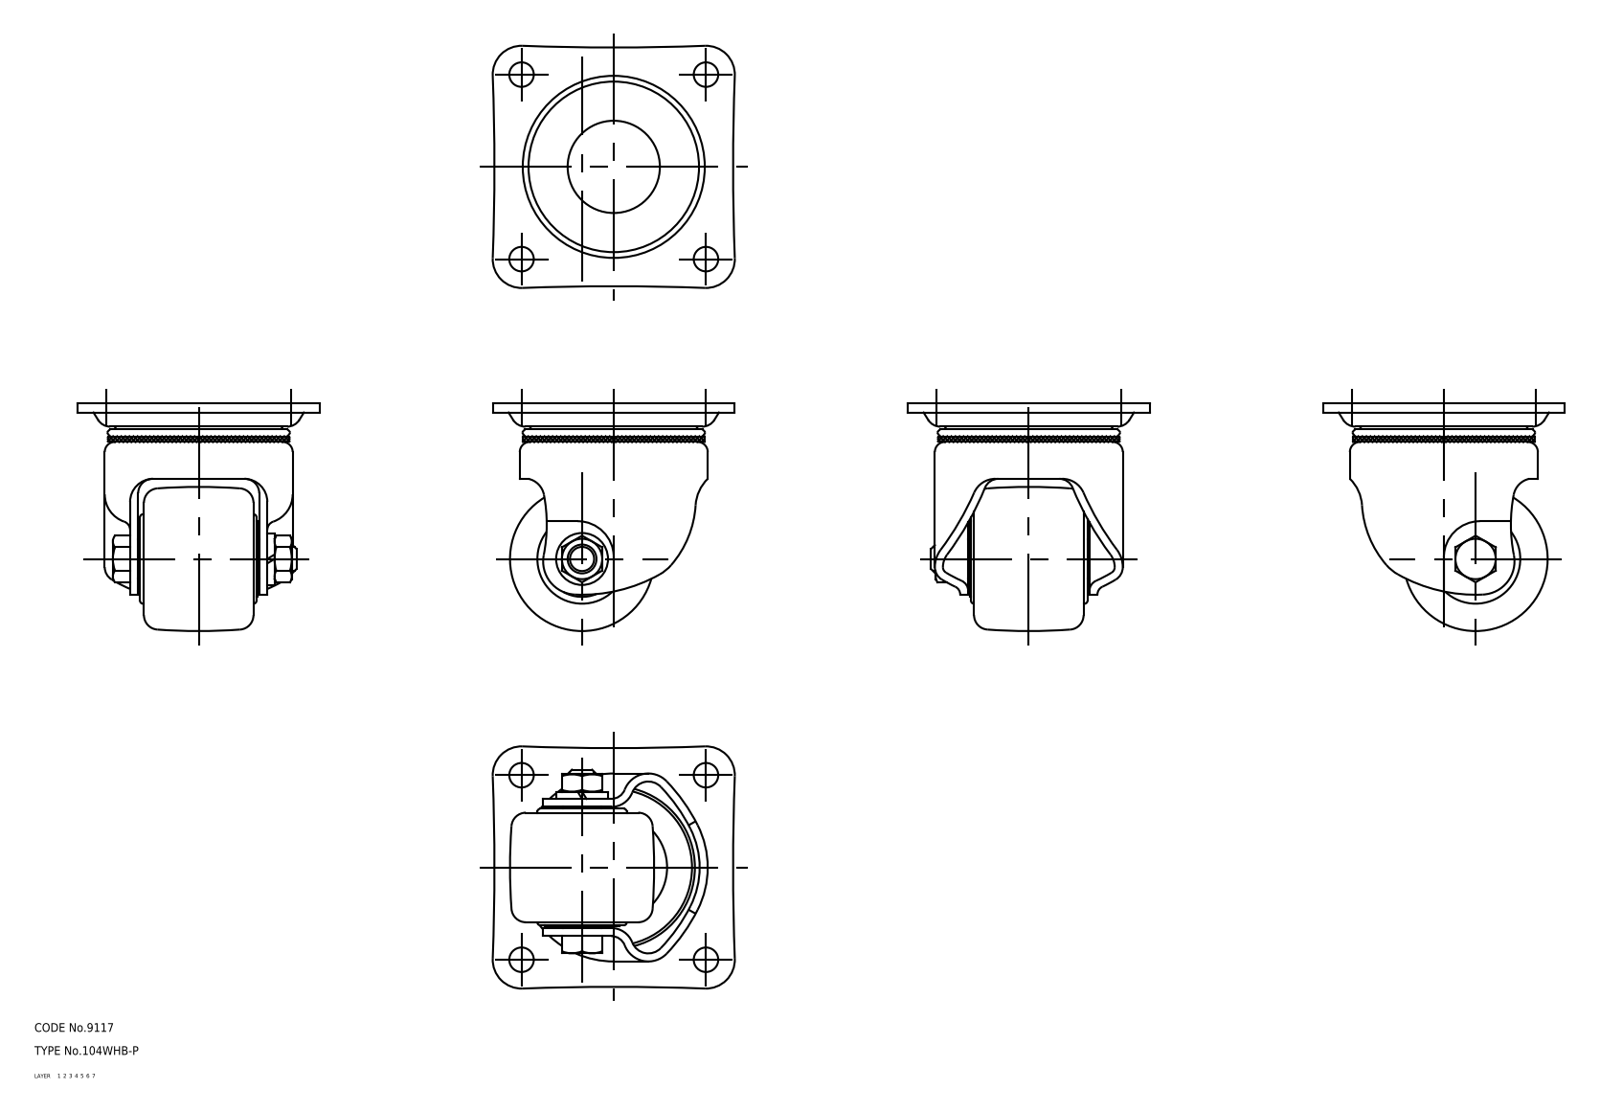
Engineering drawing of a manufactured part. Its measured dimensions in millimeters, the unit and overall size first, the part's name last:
Units: millimetres
Overall size (bounding box): 84 × 84 × 79
Volume: 172 066 mm³ · Surface area: 56 716 mm²
Bodies: 5 solids, 267 faces (0 planar, 0 cylindrical, 267 other)
Part name (STEP PRODUCT): 67128227; 67128240; 67128253; 67128266 (+1 more)
STEP written by: CADfix (AUTOMOTIVE_DESIGN)
